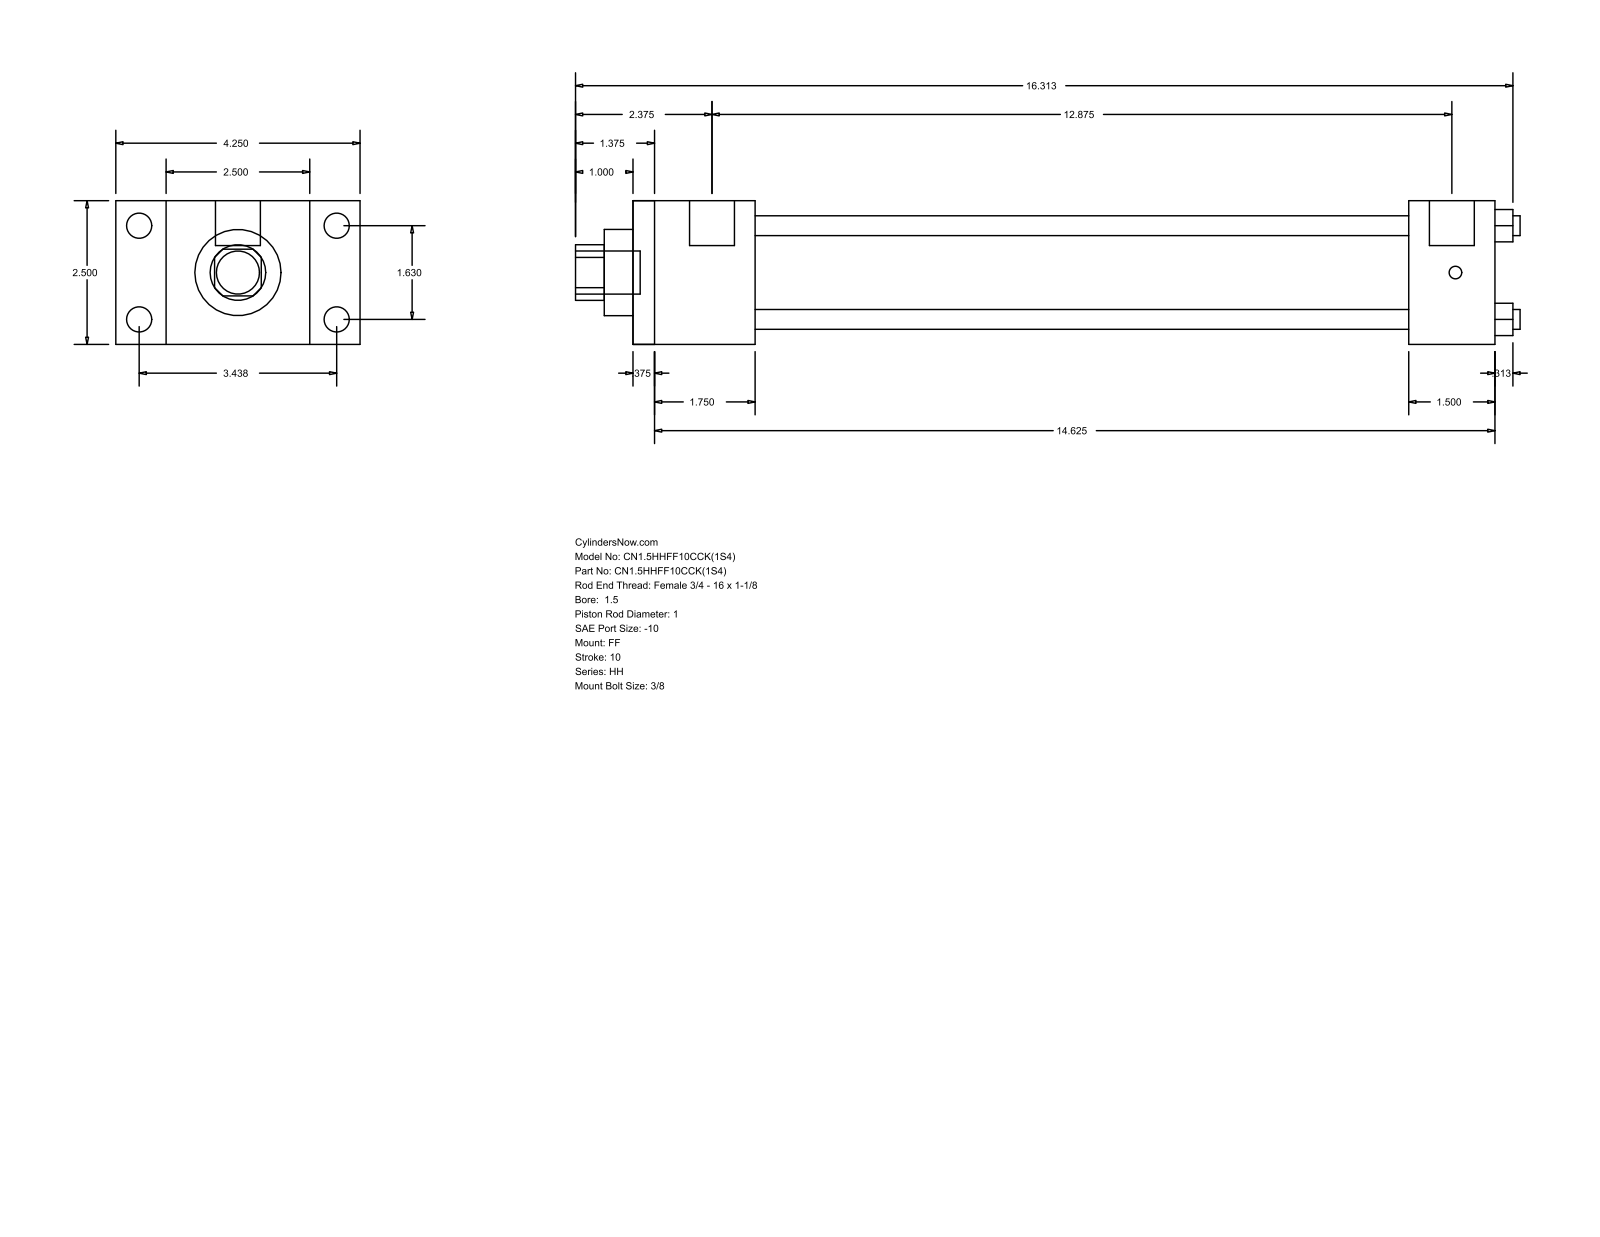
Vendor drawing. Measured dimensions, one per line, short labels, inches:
name: HH_FF__0150_1
written by: GSSL Pune (CONFIG_CONTROL_DESIGN)
unit: in
bodies: 0 solids, 92 faces (64 planar, 28 cylindrical, 0 other)
size: 16.437 × 4.25 × 2.5
holes: 4× ⌀0.345, 1× ⌀1, 1× ⌀1.5, 1× ⌀1.75
bosses: 4× ⌀0.438, 4× ⌀0.219, 2× ⌀0.781, 1× ⌀0.75
rounds: 1× R0.484
face distances: 2.5, 15, 0.375, 14.625, 2.125, 1.75, 12.875, 13.5, 13.125, 11.375
hole spacings: 1.152, 1.63, 2.305
